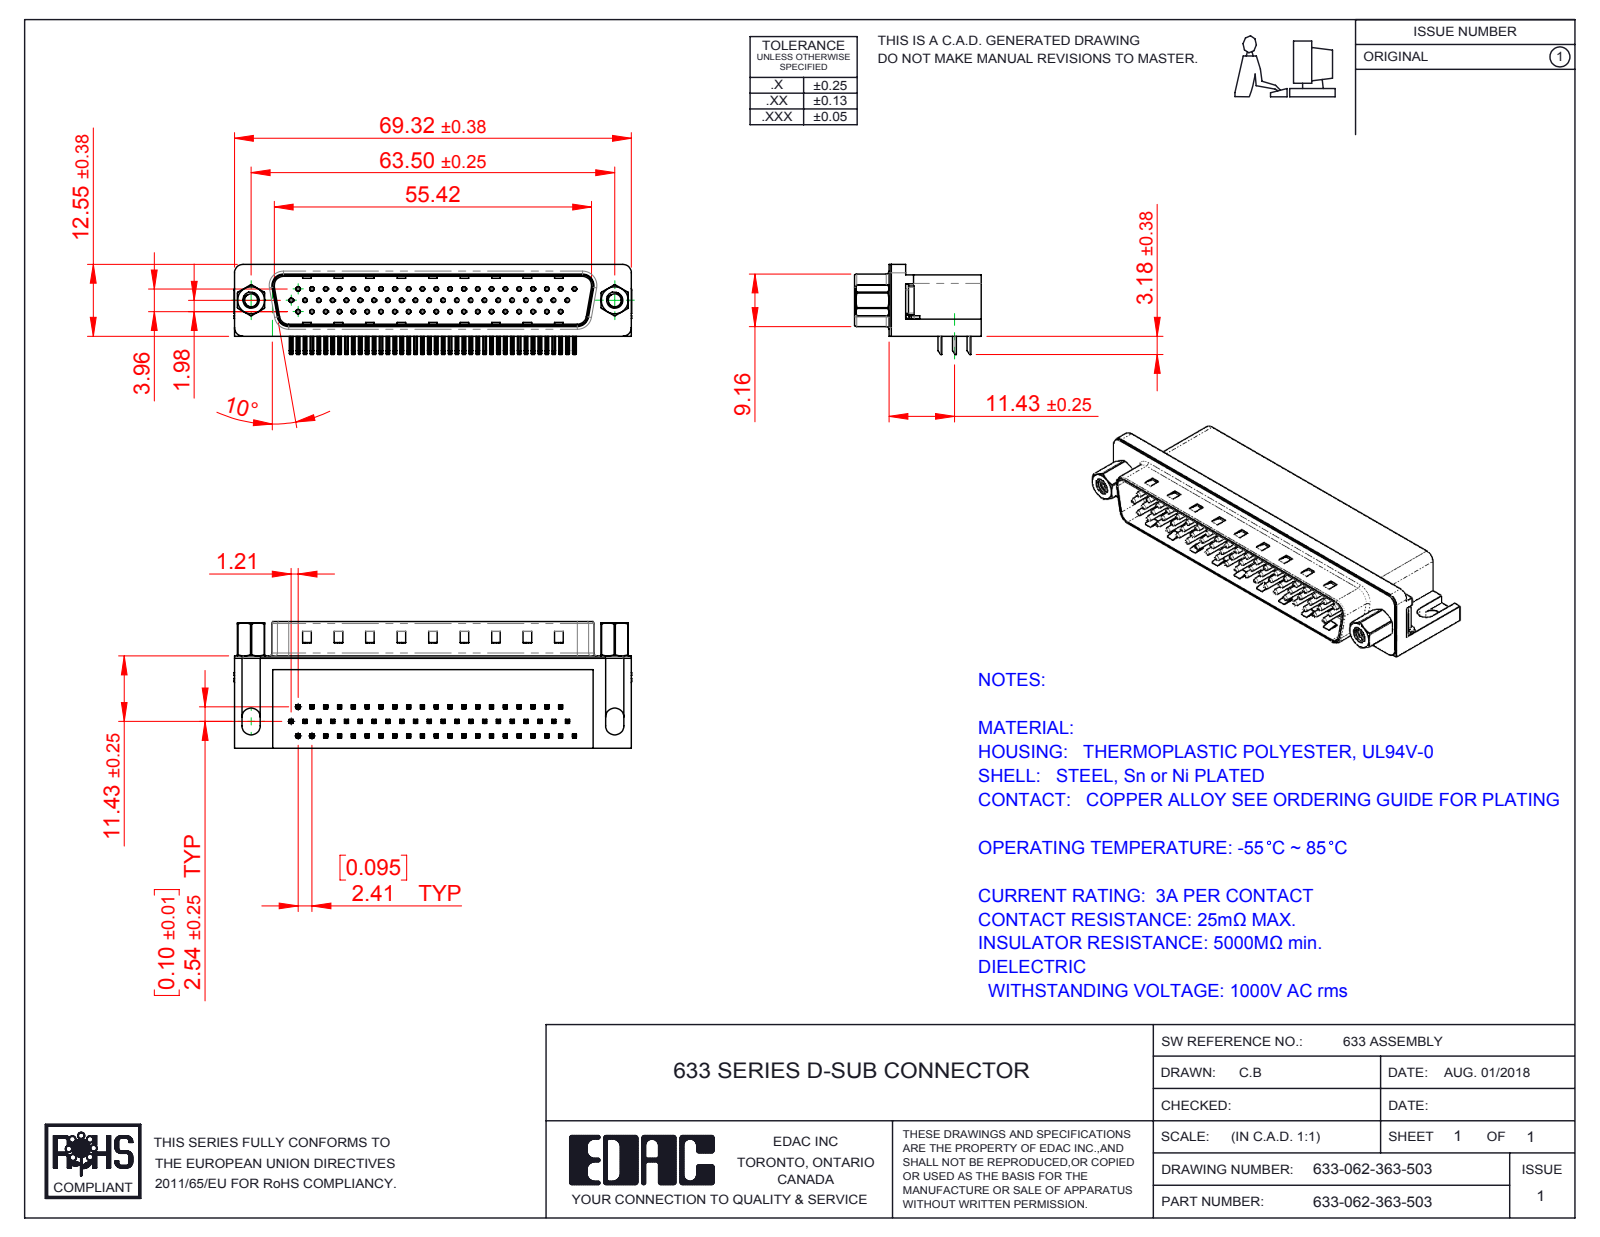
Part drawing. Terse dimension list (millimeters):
name: 633 Contact Bottom; 633 Housing_62 Contact; 633-062-363-503; 633 Shell_62 Contact (+5 more)
written by: SolidWorks 2016 (CONFIG_CONTROL_DESIGN)
unit: mm
bodies: 70 solids, 5192 faces (3235 planar, 1502 cylindrical, 455 other)
size: 69.4 × 22.1 × 15.73
volume: 11 209 mm³; area: 13 635 mm²
holes: 62× ⌀0.35, 62× ⌀0.8, 2× ⌀2.26, 2× ⌀2.29, 2× ⌀4, 2× ⌀4.8, 2× ⌀5
bosses: 62× ⌀0.75, 2× ⌀4.9, 2× ⌀4.75, 2× ⌀3.9, 2× ⌀2.79
rounds: 256× R0.25, 124× R0.12, 16× R1, 9× R0.5, 8× R1.6, 7× R1.5, 4× R0.9, 4× R2
face distances: 0.4, 10.35, 15.7, 8.76, 2.5, 2.54, 2.9, 8.36, 16.1, 2.1
hole spacings: 2.41, 4.82, 7.24, 9.65, 14.48, 16.89, 4.83, 7.23
